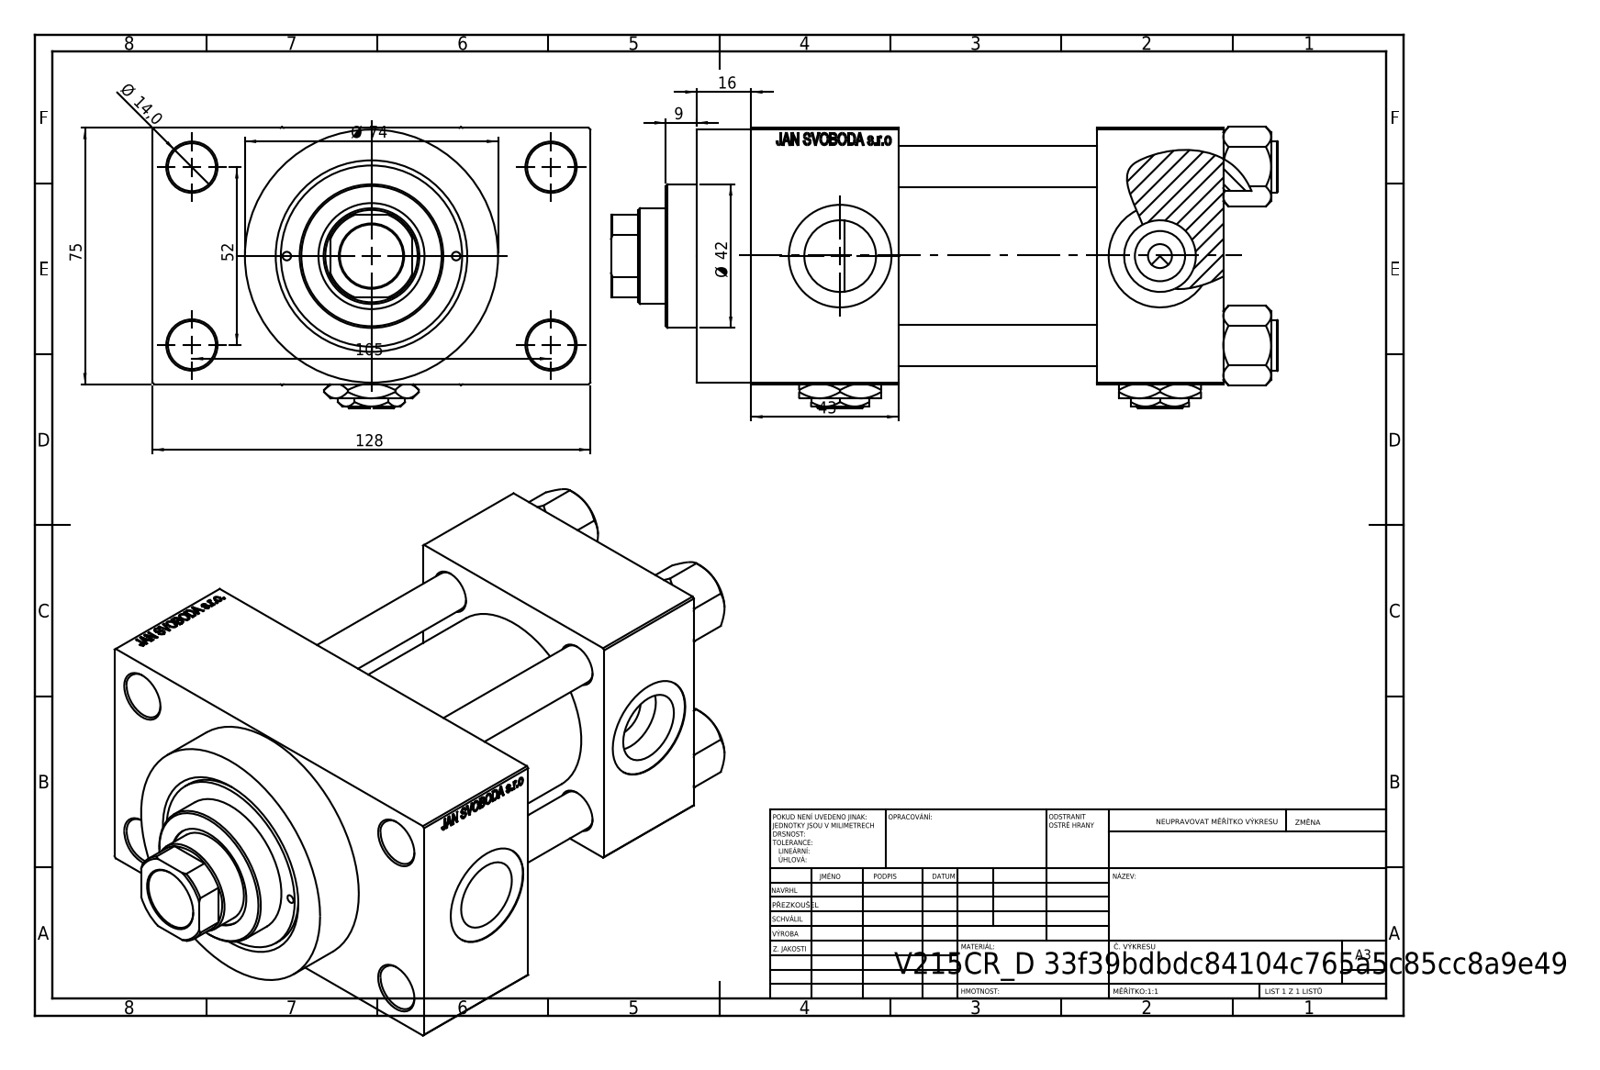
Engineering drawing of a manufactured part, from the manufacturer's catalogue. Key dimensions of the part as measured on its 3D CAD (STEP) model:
Part name (STEP PRODUCT): V215CR_D_Body; Zatka_pro_OIL_PORT; V215CR_D_TYCINKA; V215_VC_A (+2 more)
STEP written by: SolidWorks 2019 (CONFIG_CONTROL_DESIGN)
Units: millimetres
Bodies: 13 solids, 1212 faces (547 planar, 103 cylindrical, 562 other)
Overall size (bounding box): 195 × 128 × 82.27
Volume: 801 986 mm³ · Surface area: 174 663 mm²
Round holes (diameter × count): ⌀12 ×4, ⌀14 ×4, ⌀20.96 ×4, ⌀30 ×4, ⌀7 ×3, ⌀2.5 ×2, ⌀18.5 ×1, ⌀28 ×1, ⌀31 ×1, ⌀41 ×1, ⌀50 ×1, ⌀53 ×1
Round bosses / shafts (diameter × count): ⌀15 ×4, ⌀74 ×1, ⌀56 ×1, ⌀42 ×1
Partial cylindrical surfaces — rounded edges, fillets, slot ends (radius × count): R13.5 ×1
Main face-to-face distances: 75, 58, 37, 95, 26.5, 138, 101, 43, 101.5, 16
Hole centre spacings: 26.19, 26.35, 36.98, 38.03, 52.3, 57.22, 58.43, 58.59
